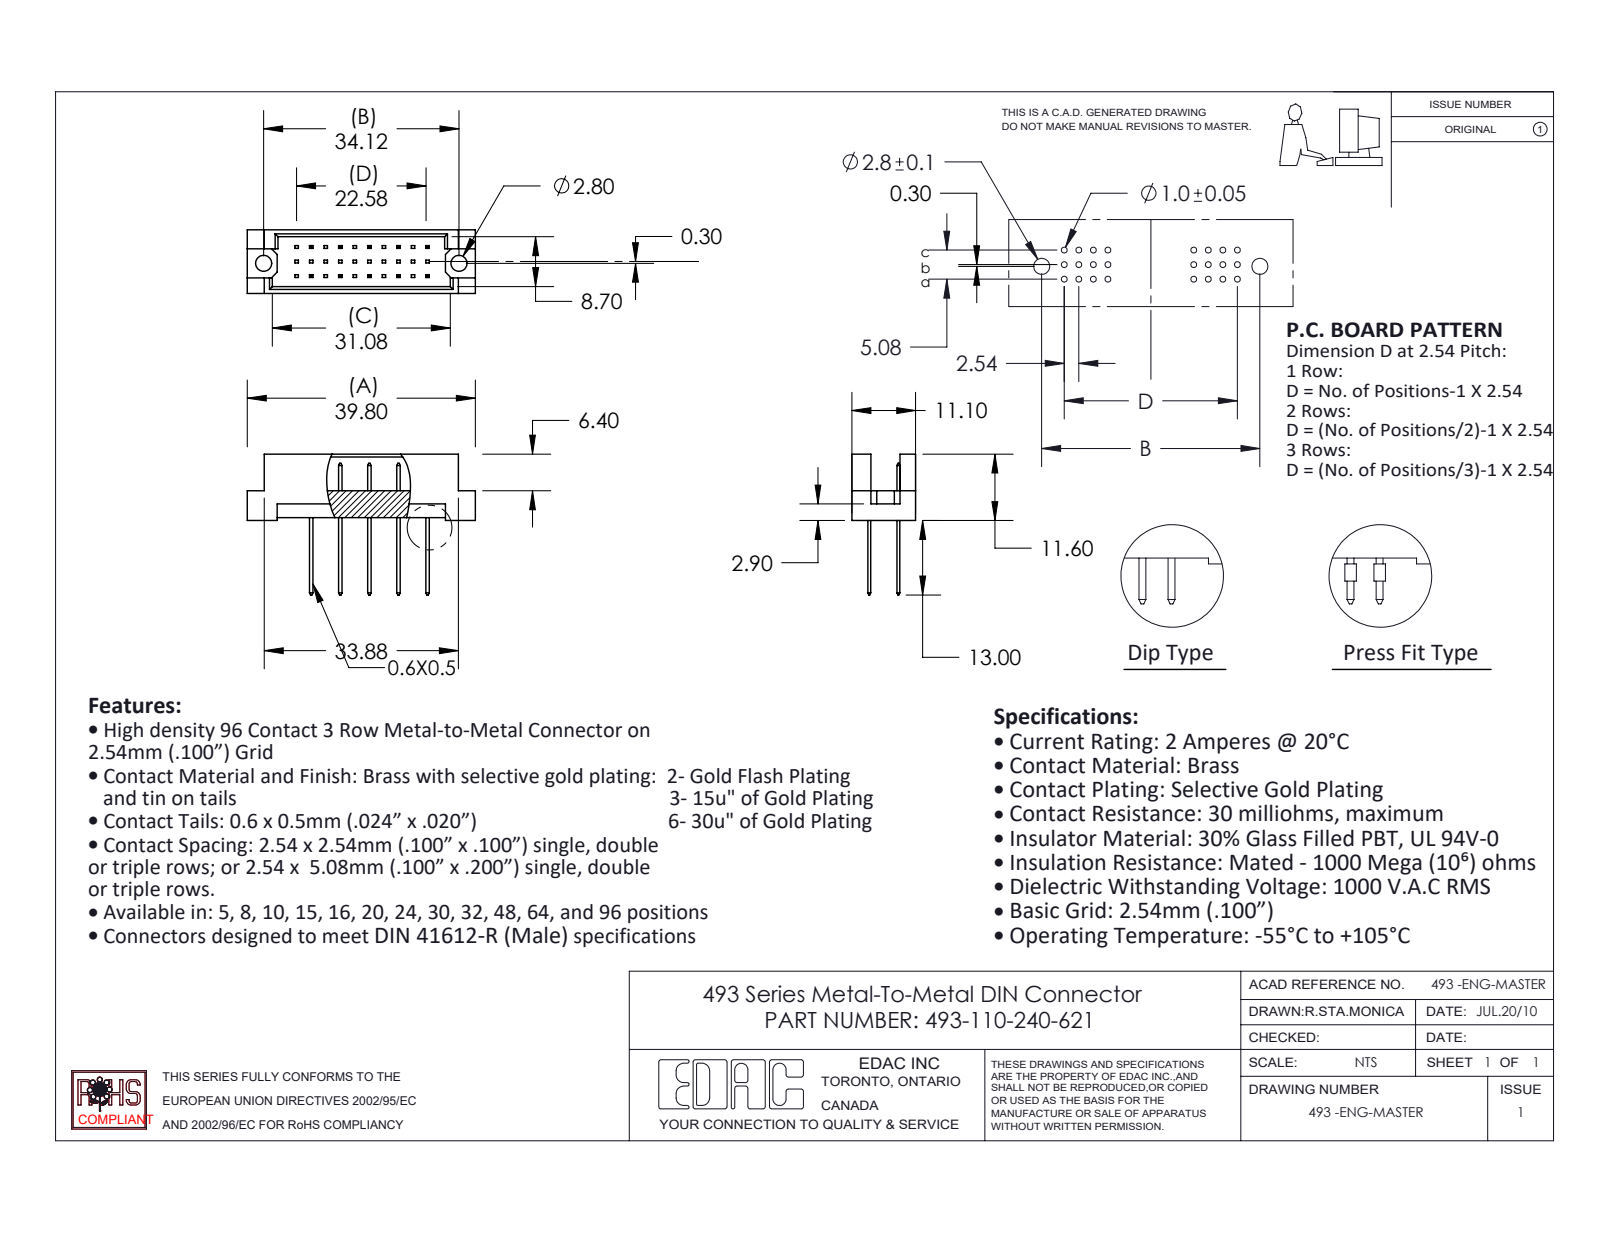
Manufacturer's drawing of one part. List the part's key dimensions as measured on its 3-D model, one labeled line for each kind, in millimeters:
Part name (STEP PRODUCT): 493 Part_30; 493-290_40; 493-110-240-622
STEP written by: SolidWorks 2020 (CONFIG_CONTROL_DESIGN)
Units: millimetres
Bodies: 11 solids, 312 faces (308 planar, 4 cylindrical, 0 other)
Overall size (bounding box): 39.8 × 24.6 × 11.1
Volume: 2 441 mm³ · Surface area: 3 240 mm²
Round holes (diameter × count): ⌀2.8 ×2
Main face-to-face distances: 1.2, 9.9, 5.08, 11.1, 0.5, 8.7, 4.7, 2.76, 3.26, 7.84
Hole centre spacings: 34.12
